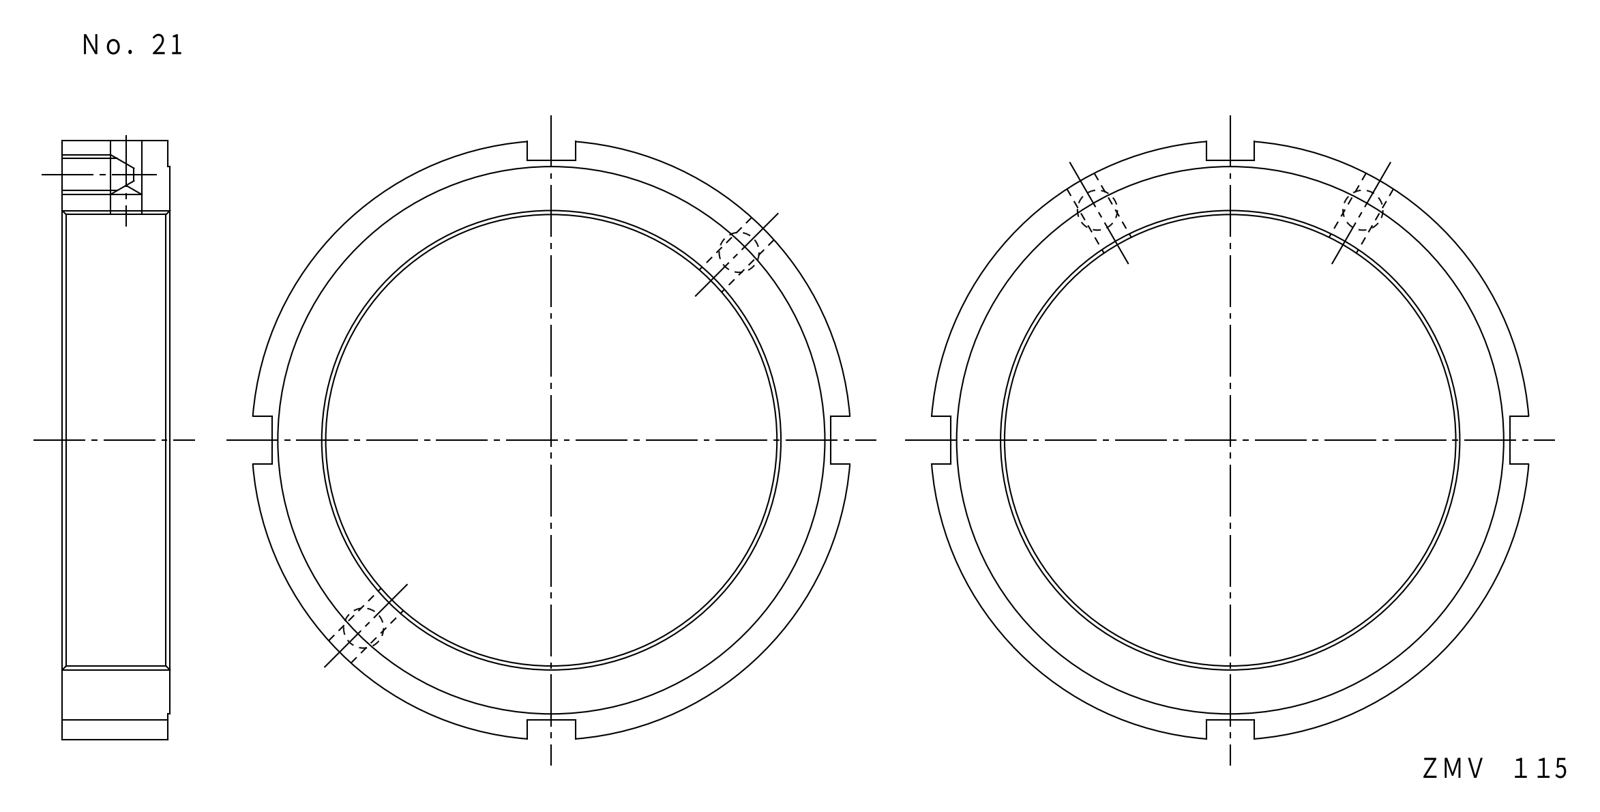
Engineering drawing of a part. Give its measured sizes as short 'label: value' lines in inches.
name: FKD ZMV115
written by: Autodesk Inventor LT (CONFIG_CONTROL_DESIGN)
unit: in
bodies: 1 solid, 29 faces (15 planar, 10 cylindrical, 4 other)
size: 5.887 × 5.887 × 1.063
volume: 11.34 in³; area: 59.99 in²
holes: 2× ⌀0.311, 2× ⌀0.33, 1× ⌀4.528
bosses: 1× ⌀5.906, 1× ⌀5.394
face distances: 1.063, 0.02, 1.043, 2.52, 2.992, 5.512, 0.472
hole spacings: 2.618, 5.236
